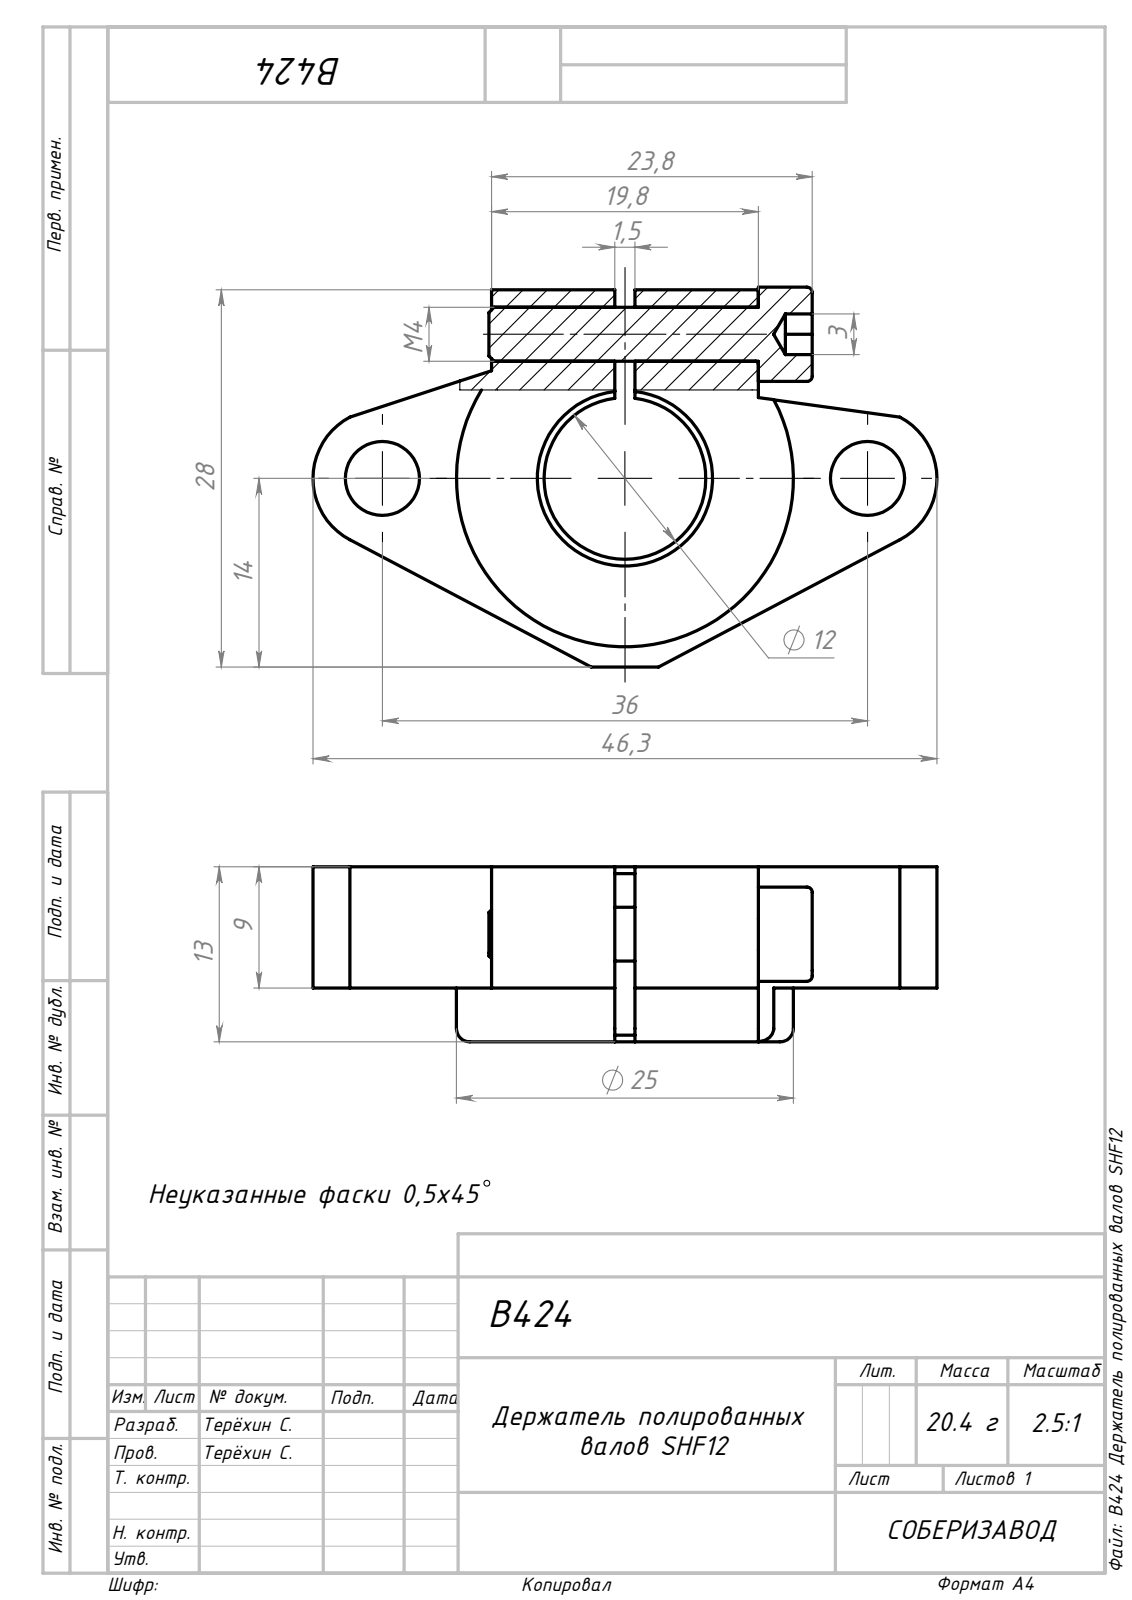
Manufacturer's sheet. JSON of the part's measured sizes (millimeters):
{"part_name": "socket head cap screw_din_DIN 912 M4 x 20 --- 20N; B424 Держатель полированных валов SHF12_00", "step_written_by": "SolidWorks 2022 (AUTOMOTIVE_DESIGN)", "units": "millimeters", "bodies": {"solids": 2, "faces": 69, "planar": 30, "cylindrical": 22, "other": 17}, "overall_size": [46.3, 28.2, 13], "volume_mm3": 7573, "surface_area_mm2": 4269, "round_holes": [[5.5, 2], [4, 1], [12, 1]], "round_bosses_or_shafts": [[25, 1], [7, 1]], "partial_cylinders_radius": [[5.15, 2]], "face_to_face_distances": [4, 9, 13, 9.15, 10.65, 1.5, 28, 19.8, 23.8, 14.65], "hole_center_spacings": [18, 36]}
